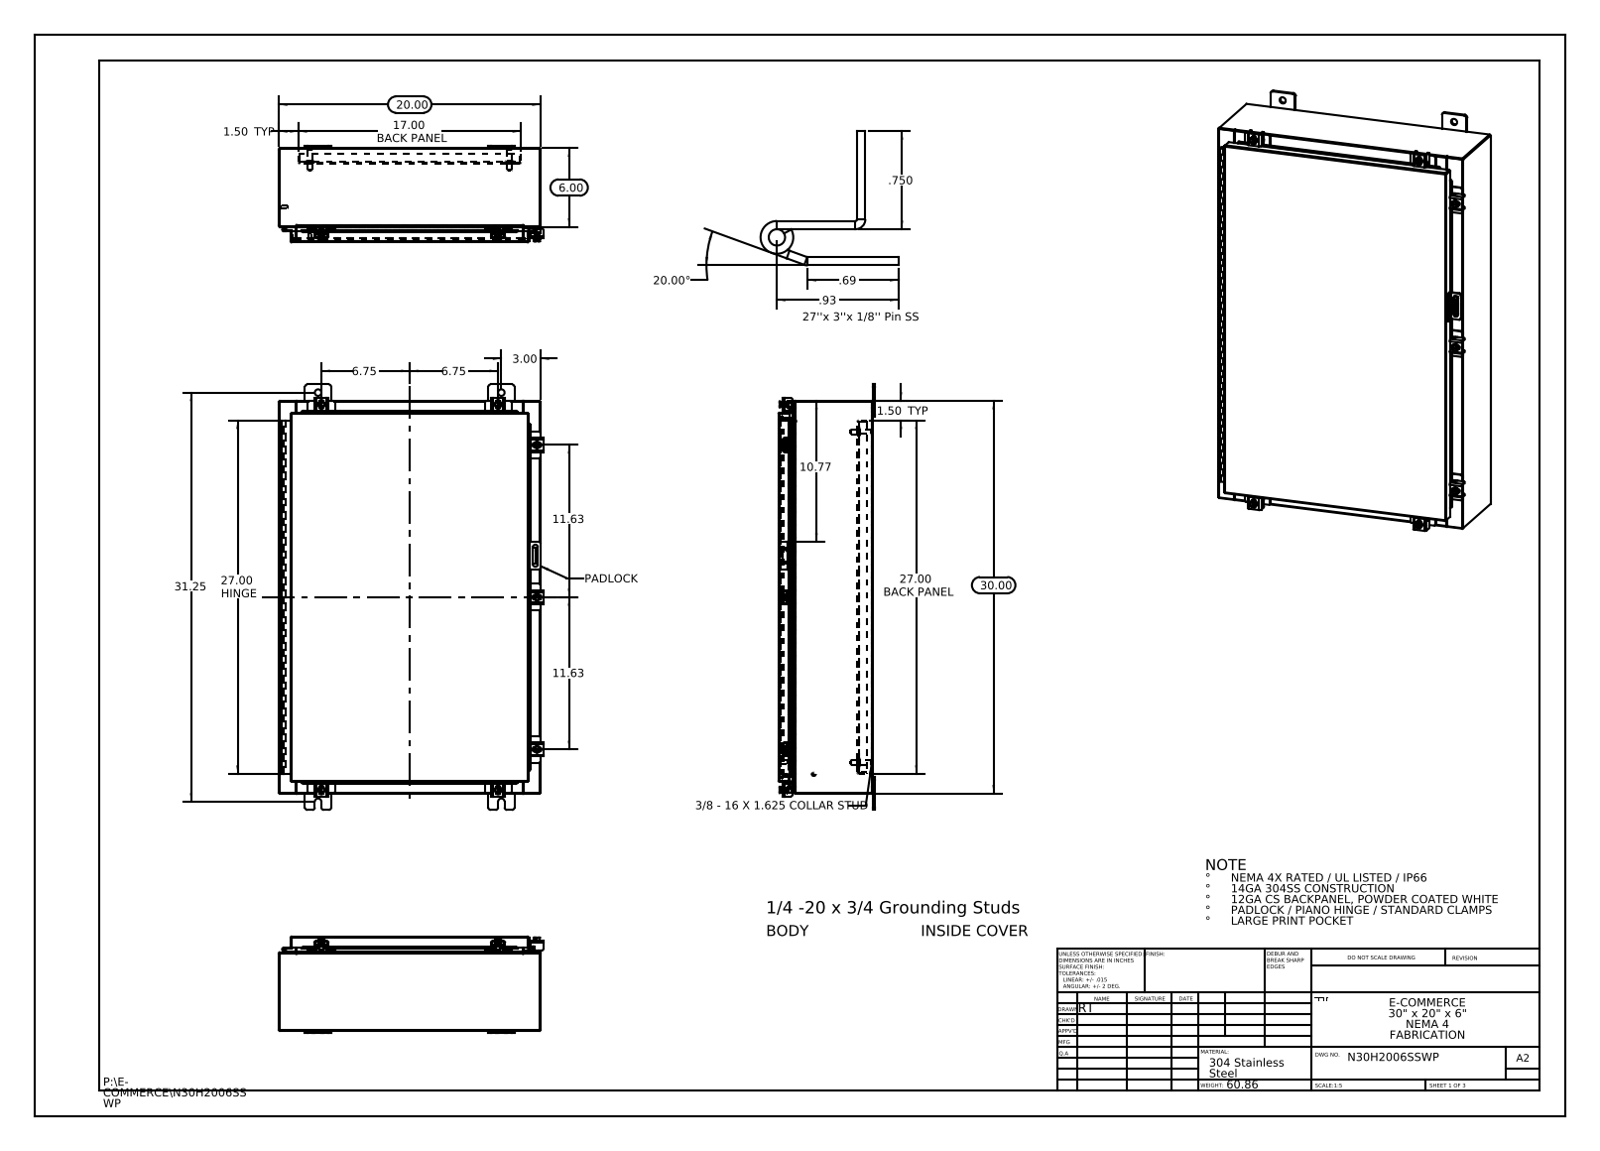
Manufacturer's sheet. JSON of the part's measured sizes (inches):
{"part_name": "N30H2006SSWP Padlock Hasp; N30H2006SSWP Clamp Assembly; Quarter-20 CD Stud; N30H2006SSWP Hinge Cover Side (+8 more)", "step_written_by": "SolidWorks 2013 (CONFIG_CONTROL_DESIGN)", "units": "inches", "bodies": {"solids": 54, "faces": 2016, "planar": 1062, "cylindrical": 838, "other": 116}, "overall_size": [32.5, 20.211, 7.389], "volume_in3": 214.2, "surface_area_in2": 5348, "round_holes": [[0.5, 8], [0.213, 7], [0.26, 7], [0.125, 2]], "round_bosses_or_shafts": [[0.25, 8], [0.5, 7], [0.399, 7], [0.625, 4], [0.375, 4], [0.33, 4], [0.315, 2], [0.236, 2]], "partial_cylinders_radius": [[0.06, 34], [0.013, 27], [0.19, 24], [0.088, 21], [0.12, 14], [0.141, 14], [0.05, 11], [0.08, 10]], "face_to_face_distances": [0.075, 7.126, 7.051, 7.201, 0.104, 1, 1.075, 6.051, 6.126, 1.179], "hole_center_spacings": [27.365, 30.898, 0.431, 0.934, 1.858, 2.275, 2.276, 2.327]}
